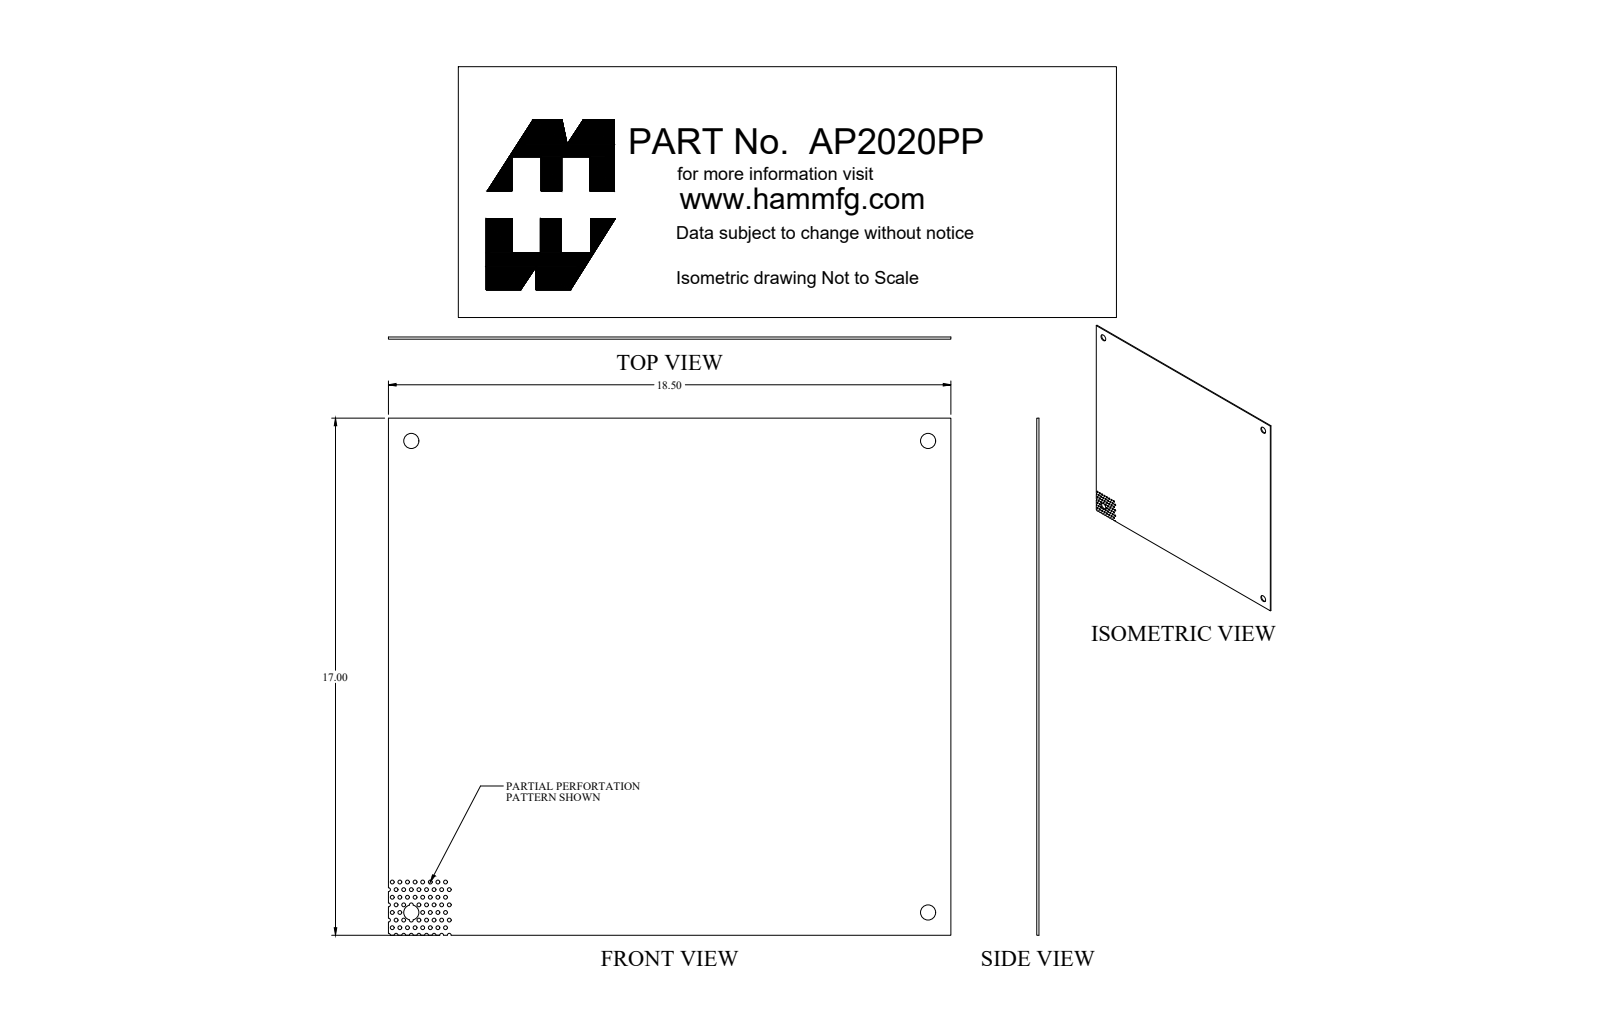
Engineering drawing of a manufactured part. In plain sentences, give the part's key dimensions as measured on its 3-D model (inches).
The part is named "AP2020PP_Default". Its 3-D file was written by "SolidWorks 2019 (CONFIG_CONTROL_DESIGN)". It is 1 solid with 152 faces: 17 planar, 135 cylindrical and 0 other. Overall it measures 18.5 by 17 by 0.072 inches. Its volume is 22.54 cubic inches and its surface area 633.1 square inches. Round holes: 52 of diameter 0.125, 4 of diameter 0.5. Partial cylindrical surfaces (rounded edges, fillets, slot ends): 14 of radius 0.062. The main face-to-face distances are 0.072, 17, 18.5. The hole center spacings are 0.28, 0.5, 0.559, 0.25, 0.451, 1.152, 0.707, 0.76.
